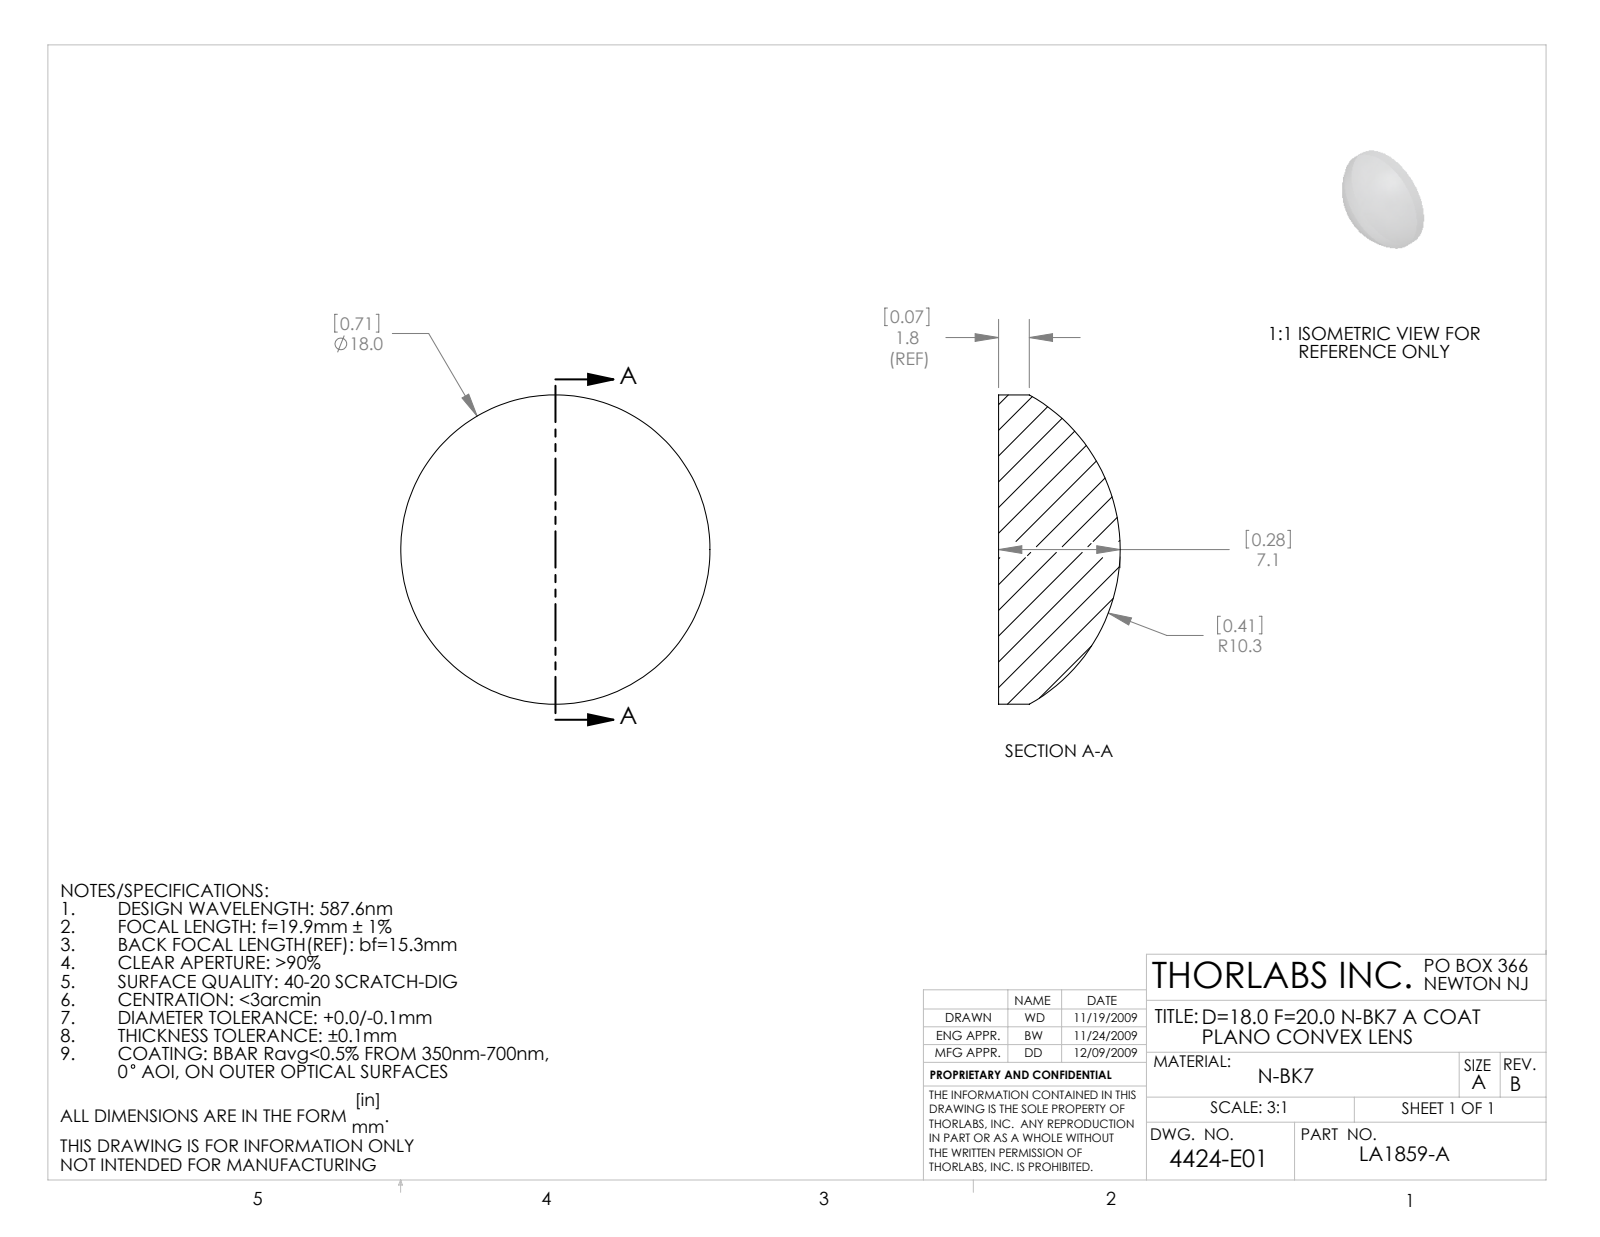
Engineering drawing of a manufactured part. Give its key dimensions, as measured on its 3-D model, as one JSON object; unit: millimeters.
{"part_name": "4424-E0W", "step_written_by": "SolidWorks 2009 (AUTOMOTIVE_DESIGN)", "units": "millimeters", "bodies": {"solids": 1, "faces": 5, "planar": 1, "cylindrical": 2, "other": 2}, "overall_size": [18, 18, 7.08], "volume_mm3": 1206, "surface_area_mm2": 698, "round_bosses_or_shafts": [[18, 1]]}
